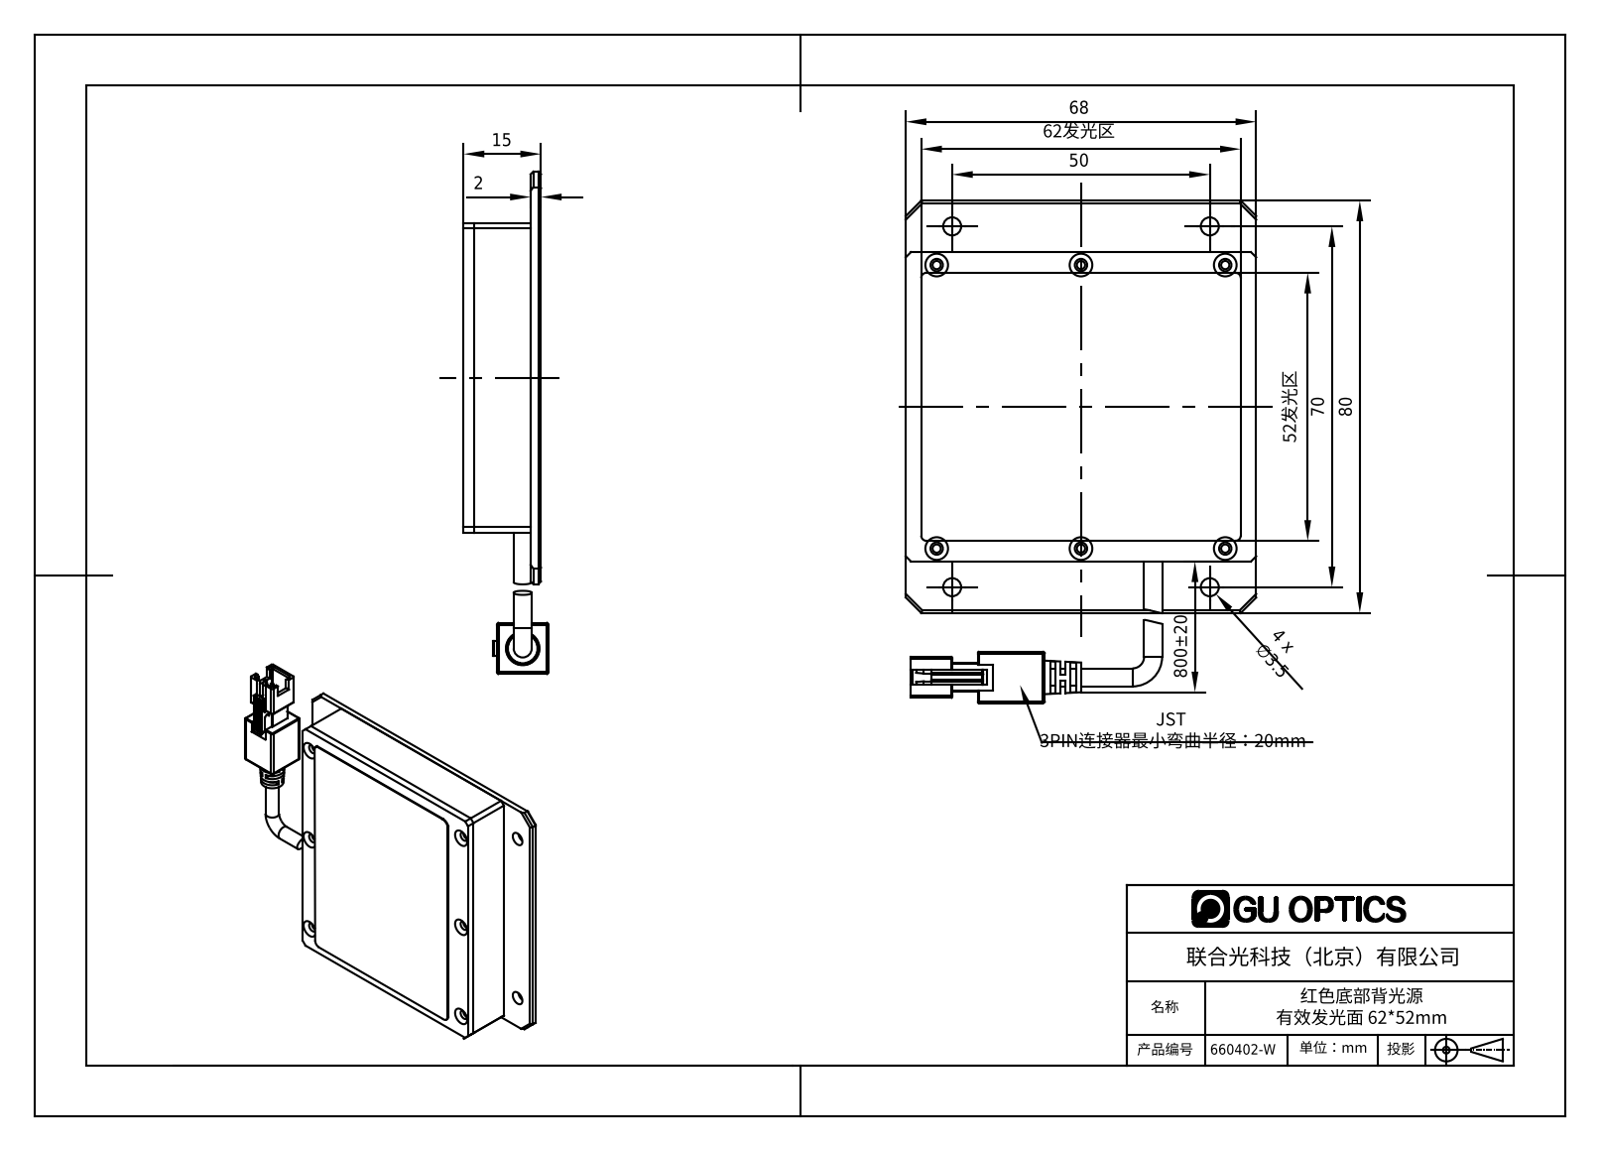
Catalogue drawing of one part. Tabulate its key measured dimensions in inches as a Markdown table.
| quantity | value |
| --- | --- |
| part name | 660402-R |
| STEP written by | SolidWorks 2016 (AUTOMOTIVE_DESIGN) |
| units | inches |
| bodies | 6 solids, 922 faces (650 planar, 137 cylindrical, 135 other) |
| overall size | 3.839 × 2.677 × 0.656 |
| volume | 2.129 in³ |
| surface area | 59.1 in² |
| round holes (diameter × count) | 0.063 × 12, 0.094 × 12, 0.138 × 4 |
| round bosses / shafts (diameter × count) | 0.138 × 2 |
| partial cylindrical surfaces (radius × count) | 0.004 × 15, 0.008 × 13, 0.016 × 12, 0.039 × 8, 0.059 × 2, 0.012 × 1, 0.027 × 1, 0.055 × 1 |
| main face-to-face distances | 0.079, 0.512, 0.433, 0.091, 0.421, 0.039, 0.52, 0.598, 0.508, 0.087 |
| hole center spacings | 1.102, 1.103, 2.456, 0.03, 2.195, 0.291, 0.318, 1.02 |
